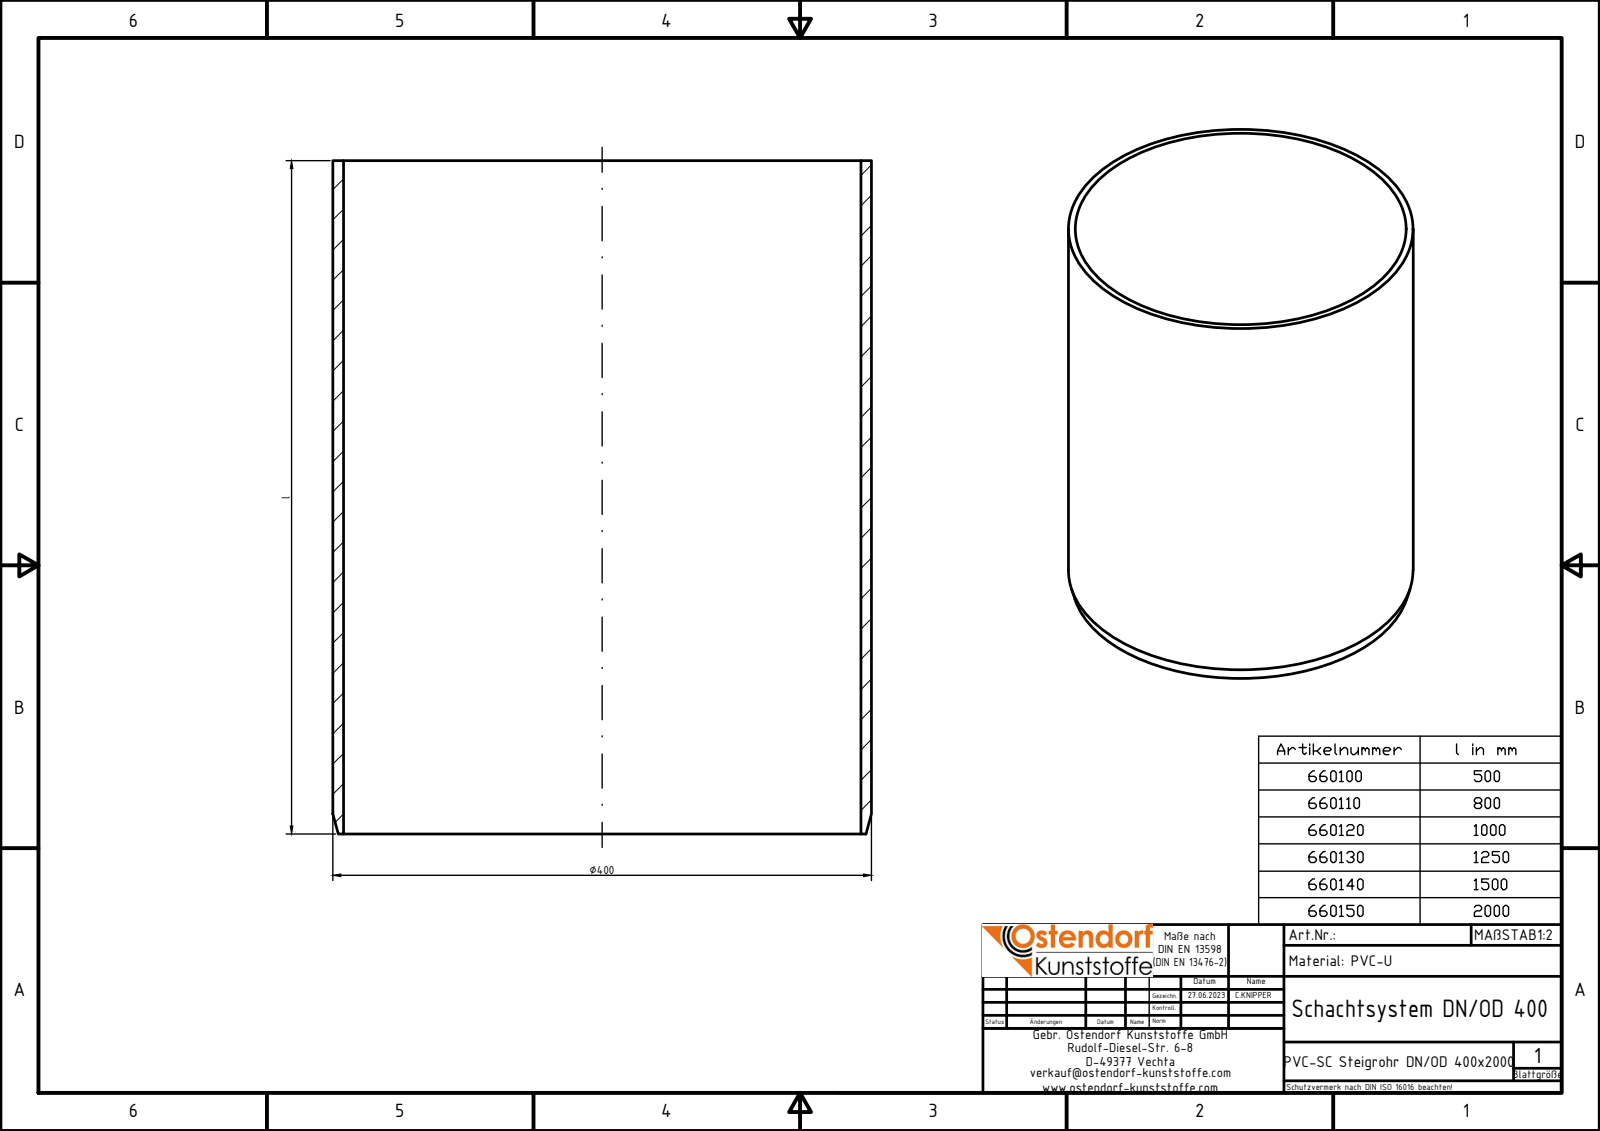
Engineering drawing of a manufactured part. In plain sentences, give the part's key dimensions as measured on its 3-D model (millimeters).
The part is named "660150". Its 3-D file was written by "Autodesk Inventor 2020 (AUTOMOTIVE_DESIGN)". It is 1 solid with 5 faces: 2 planar, 2 cylindrical and 1 other. Overall it measures 2000 by 400 by 400 millimeters. Its volume is 19 430 000 cubic millimeters and its surface area 4 942 000 square millimeters. Round holes: 1 of diameter 384.2. Round bosses or shafts: 1 of diameter 400. The main face-to-face distances are 2000.
